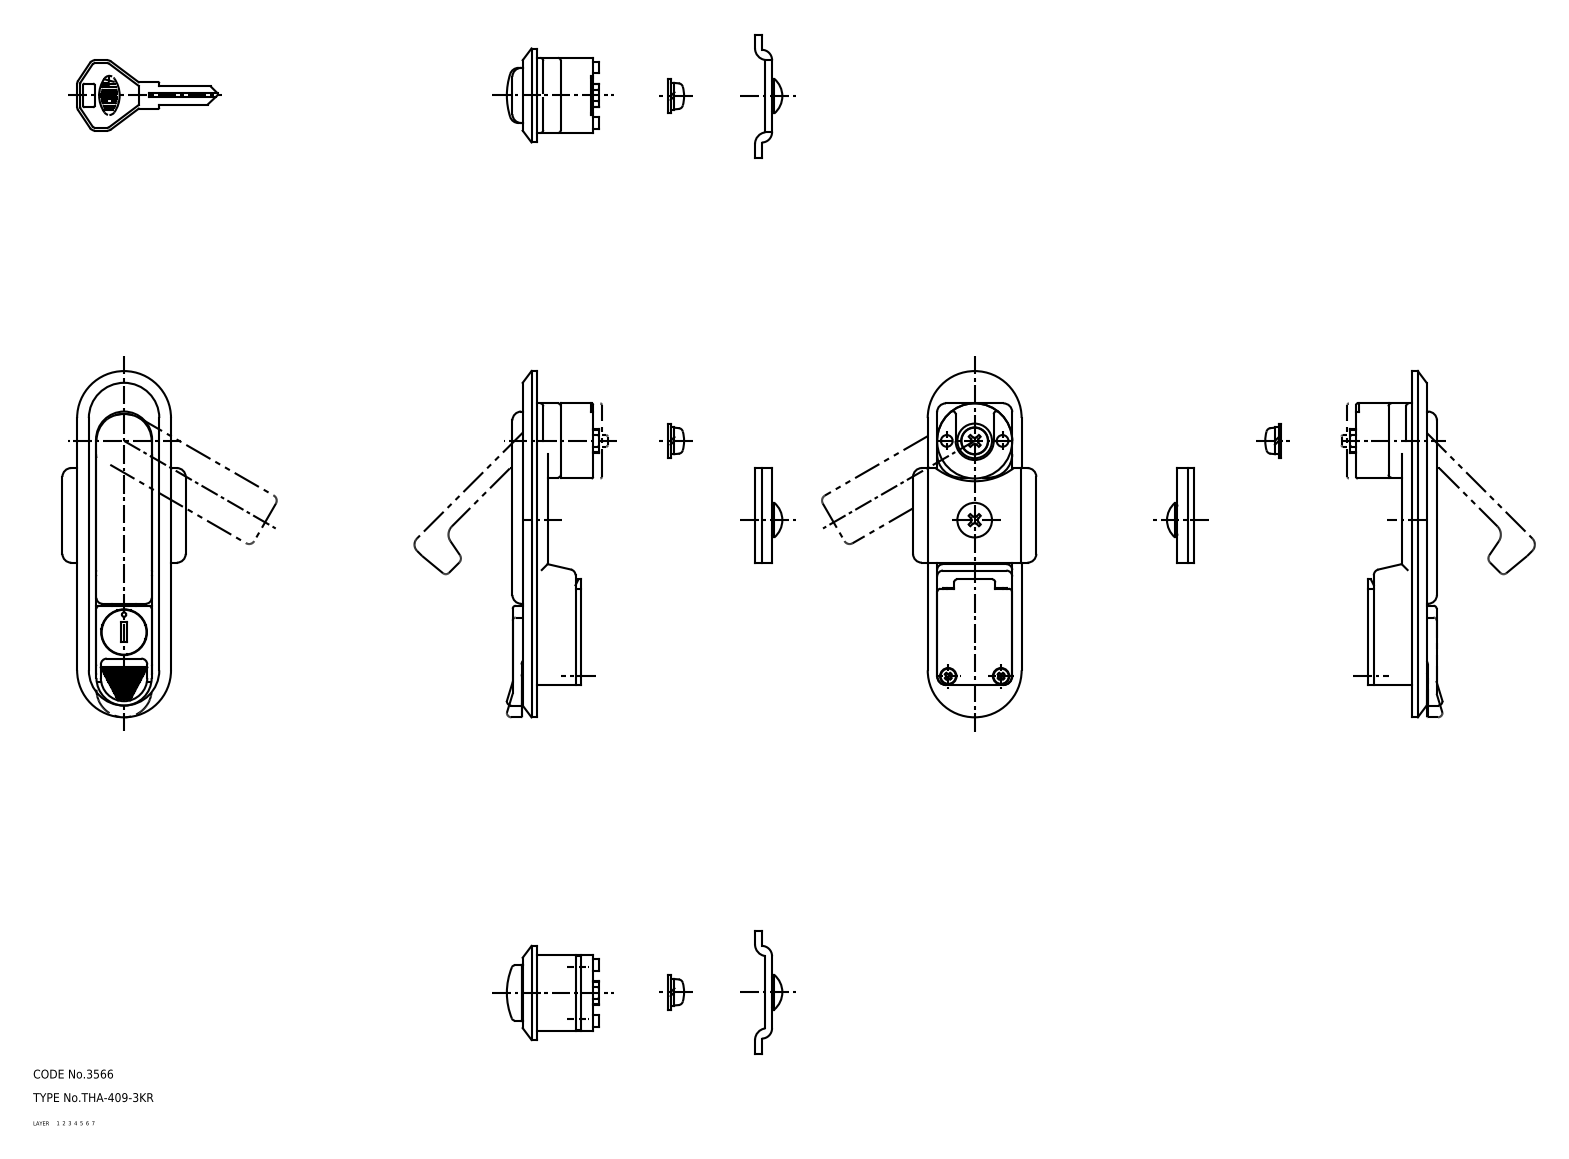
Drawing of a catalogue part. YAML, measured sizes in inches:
part_name: "THA_409_3KR"
step_written_by: "SolidWorks 2003240 (AUTOMOTIVE_DESIGN)"
units: inches
bodies: {solids: 10, faces: 397, planar: 218, cylindrical: 133, other: 46}
overall_size: [4.646, 4.605, 1.654]
volume: 2.782
surface_area: 48.42
round_holes:
  - {diameter: 0.102, count: 2}
  - {diameter: 0.197, count: 1}
  - {diameter: 0.217, count: 1}
  - {diameter: 0.315, count: 1}
  - {diameter: 0.614, count: 1}
  - {diameter: 0.752, count: 1}
  - {diameter: 0.787, count: 1}
round_bosses_or_shafts:
  - {diameter: 0.465, count: 2}
  - {diameter: 0.157, count: 2}
  - {diameter: 1.008, count: 1}
  - {diameter: 0.984, count: 1}
  - {diameter: 0.74, count: 1}
  - {diameter: 0.362, count: 1}
partial_cylinders:
  - {radius: 0.079, count: 22}
  - {radius: 0.039, count: 13}
  - {radius: 0.118, count: 11}
  - {radius: 0.02, count: 7}
  - {radius: 0.157, count: 3}
  - {radius: 0.008, count: 2}
  - {radius: 0.012, count: 2}
  - {radius: 0.138, count: 2}
face_to_face_distances: [0.138, 0.335, 0.118, 0.079, 0.197, 0.709, 0.413, 0.512, 0.63, 0.467]
hole_center_spacings: [0.689, 2.124, 3.177, 0.709, 1.063, 1.504, 2.567]
